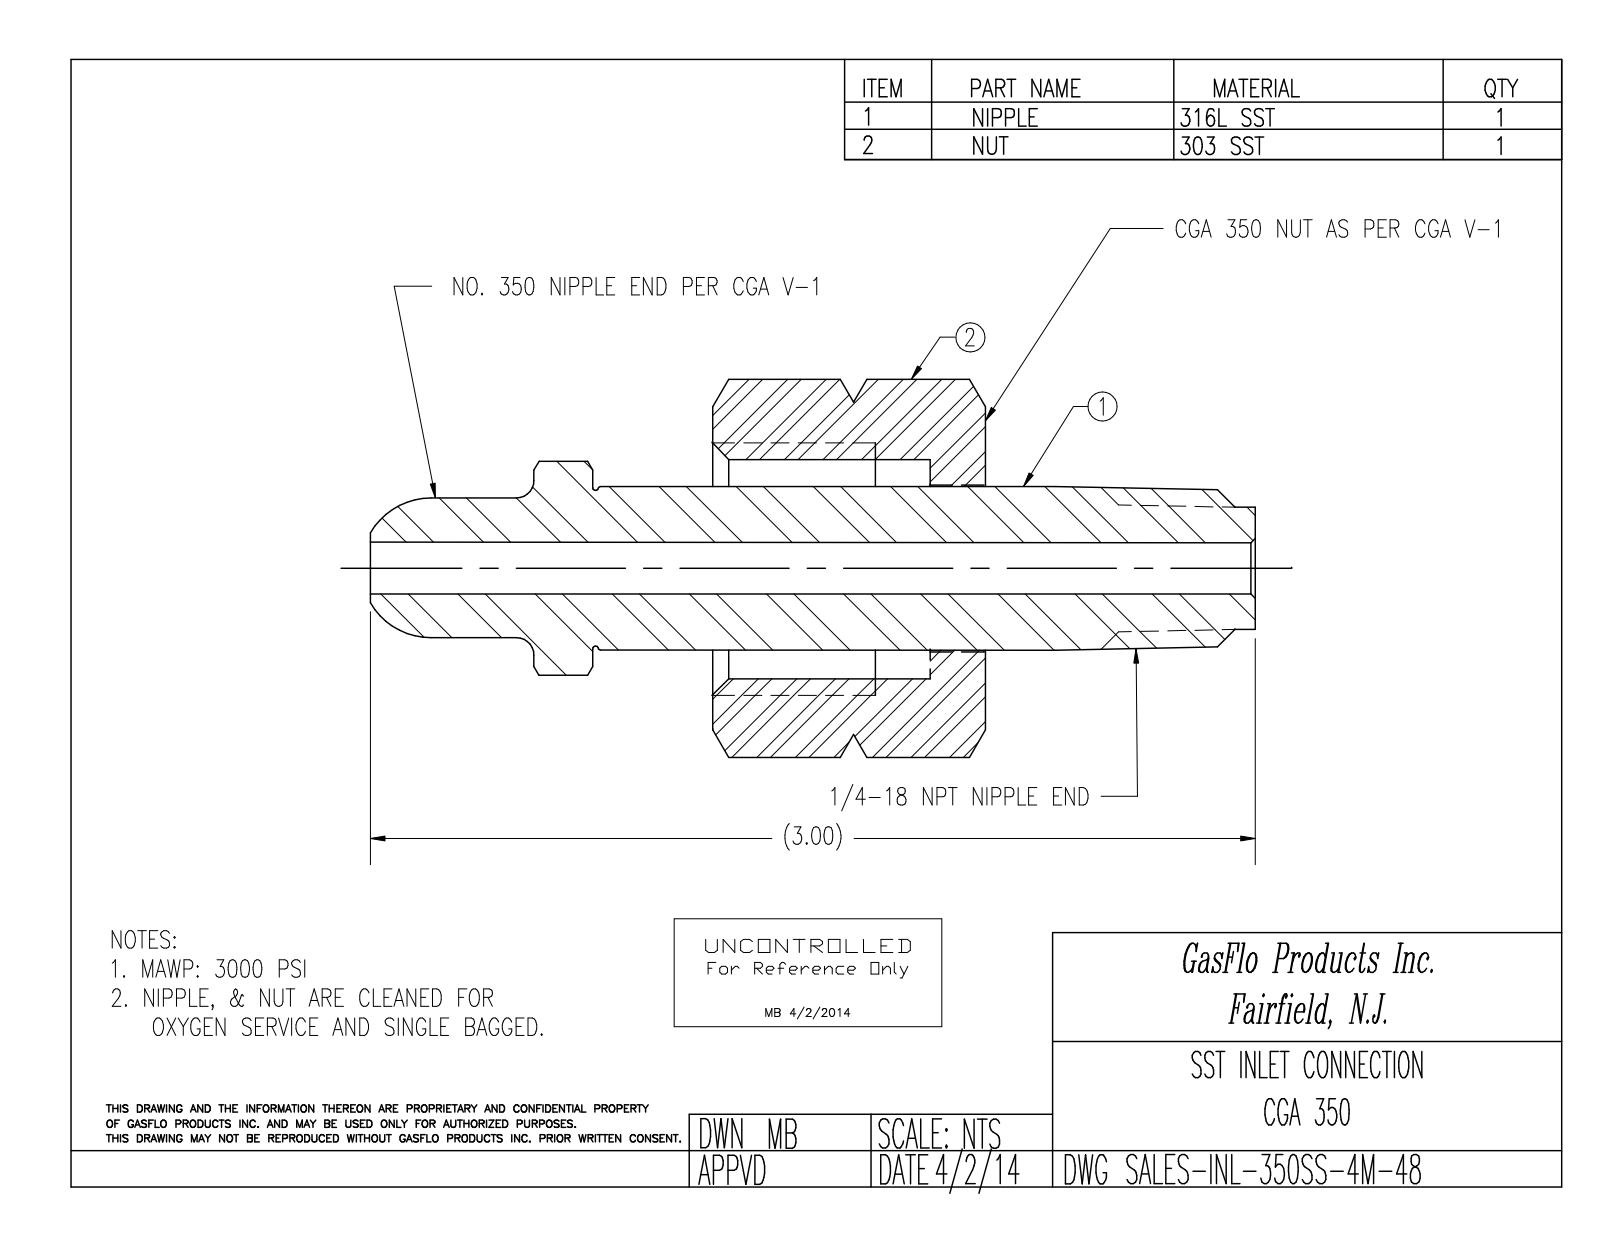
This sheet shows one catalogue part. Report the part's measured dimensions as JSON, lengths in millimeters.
{"part_name": "INL-350SS-4M-48; PRT-000079; PRT-000826", "step_written_by": "SolidWorks 2018 (CONFIG_CONTROL_DESIGN)", "units": "millimeters", "bodies": {"solids": 2, "faces": 168, "planar": 39, "cylindrical": 18, "other": 111}, "overall_size": [76.2, 33, 28.6], "volume_mm3": 20250, "surface_area_mm2": 10170, "round_holes": [[4.5, 1], [14.5, 1], [19.2, 1]], "round_bosses_or_shafts": [[14.2, 1], [13.7, 1], [12.1, 1], [10.7, 1]], "partial_cylinders_radius": [[9.3, 1]], "face_to_face_distances": [28.6, 24, 5, 19, 5.6, 23, 17.4, 52, 57, 76]}
